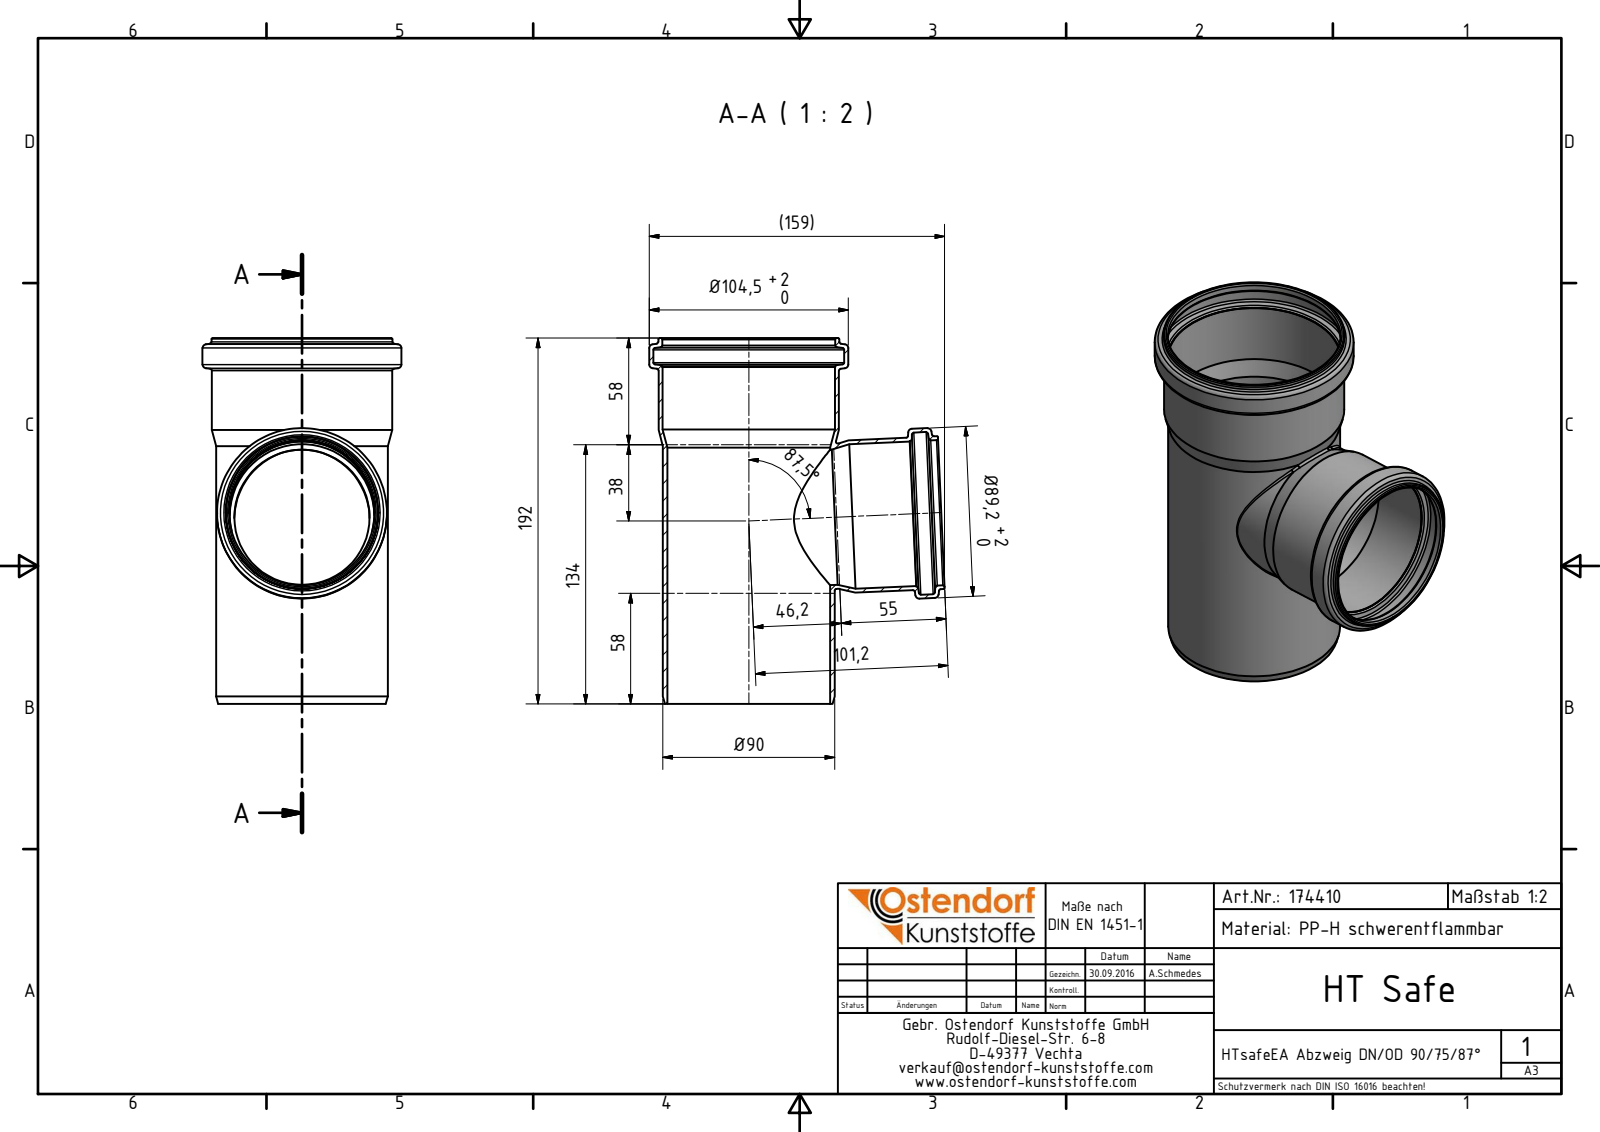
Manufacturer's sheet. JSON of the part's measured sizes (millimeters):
{"part_name": "174410 HTsafeEA DN_OD 90_75_87°", "step_written_by": "Autodesk Inventor 2016 (AUTOMOTIVE_DESIGN)", "units": "millimeters", "bodies": {"solids": 1, "faces": 60, "planar": 5, "cylindrical": 18, "other": 37}, "overall_size": [192, 155.08, 104.5], "volume_mm3": 155161, "surface_area_mm2": 140485, "round_holes": [[71, 1], [76, 1], [76.3, 1], [85.2, 1], [85.4, 1], [90.5, 1], [90.8, 1], [100.3, 1]], "round_bosses_or_shafts": [[104.5, 1], [95, 1], [94.7, 1], [90.2, 1], [89.2, 1], [80.3, 1], [80, 1], [75.2, 1]], "face_to_face_distances": [192, 176.79, 15.21, 14.9]}
